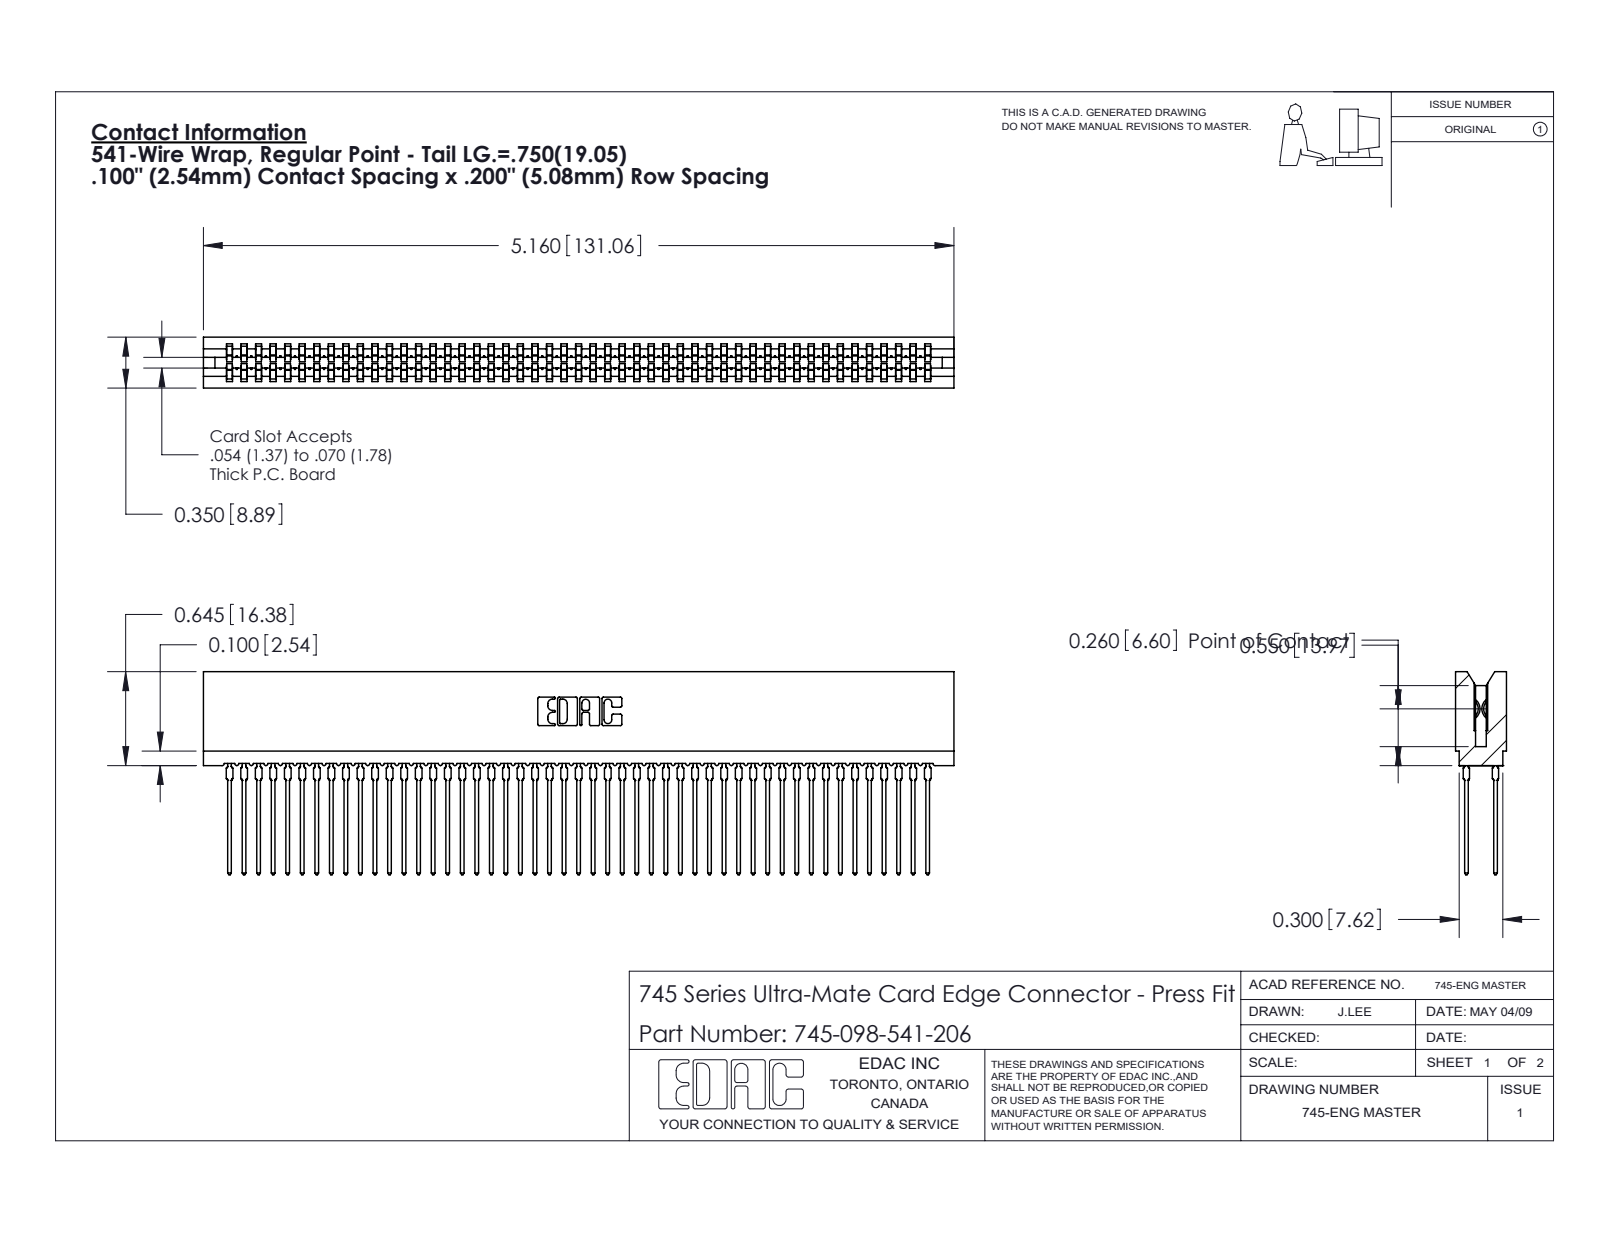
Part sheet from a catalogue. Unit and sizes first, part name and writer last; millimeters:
Units: millimetres
Overall size (bounding box): 131.1 × 35.5 × 8.9
Partial cylindrical surfaces — rounded edges, fillets, slot ends (radius × count): R0.5 ×196, R0.4 ×98, R0.3 ×22, R0.1 ×8, R0.3 ×8, R0.2 ×6, R0.8 ×6, R0.7 ×3
Main face-to-face distances: 1.6, 7.3, 5.1, 8.9, 2.2, 6.7, 0.6, 1.1, 7.7, 0.5
Volume: 12 200 mm³ · Surface area: 26 970 mm²
Bodies: 99 solids, 8867 faces (4564 planar, 1755 cylindrical, 2548 other)
Part name (STEP PRODUCT): 745-292-001_541; 745 Part_Insulator Option - 06; 745-098-541-206
STEP written by: SolidWorks 2020 (CONFIG_CONTROL_DESIGN)
